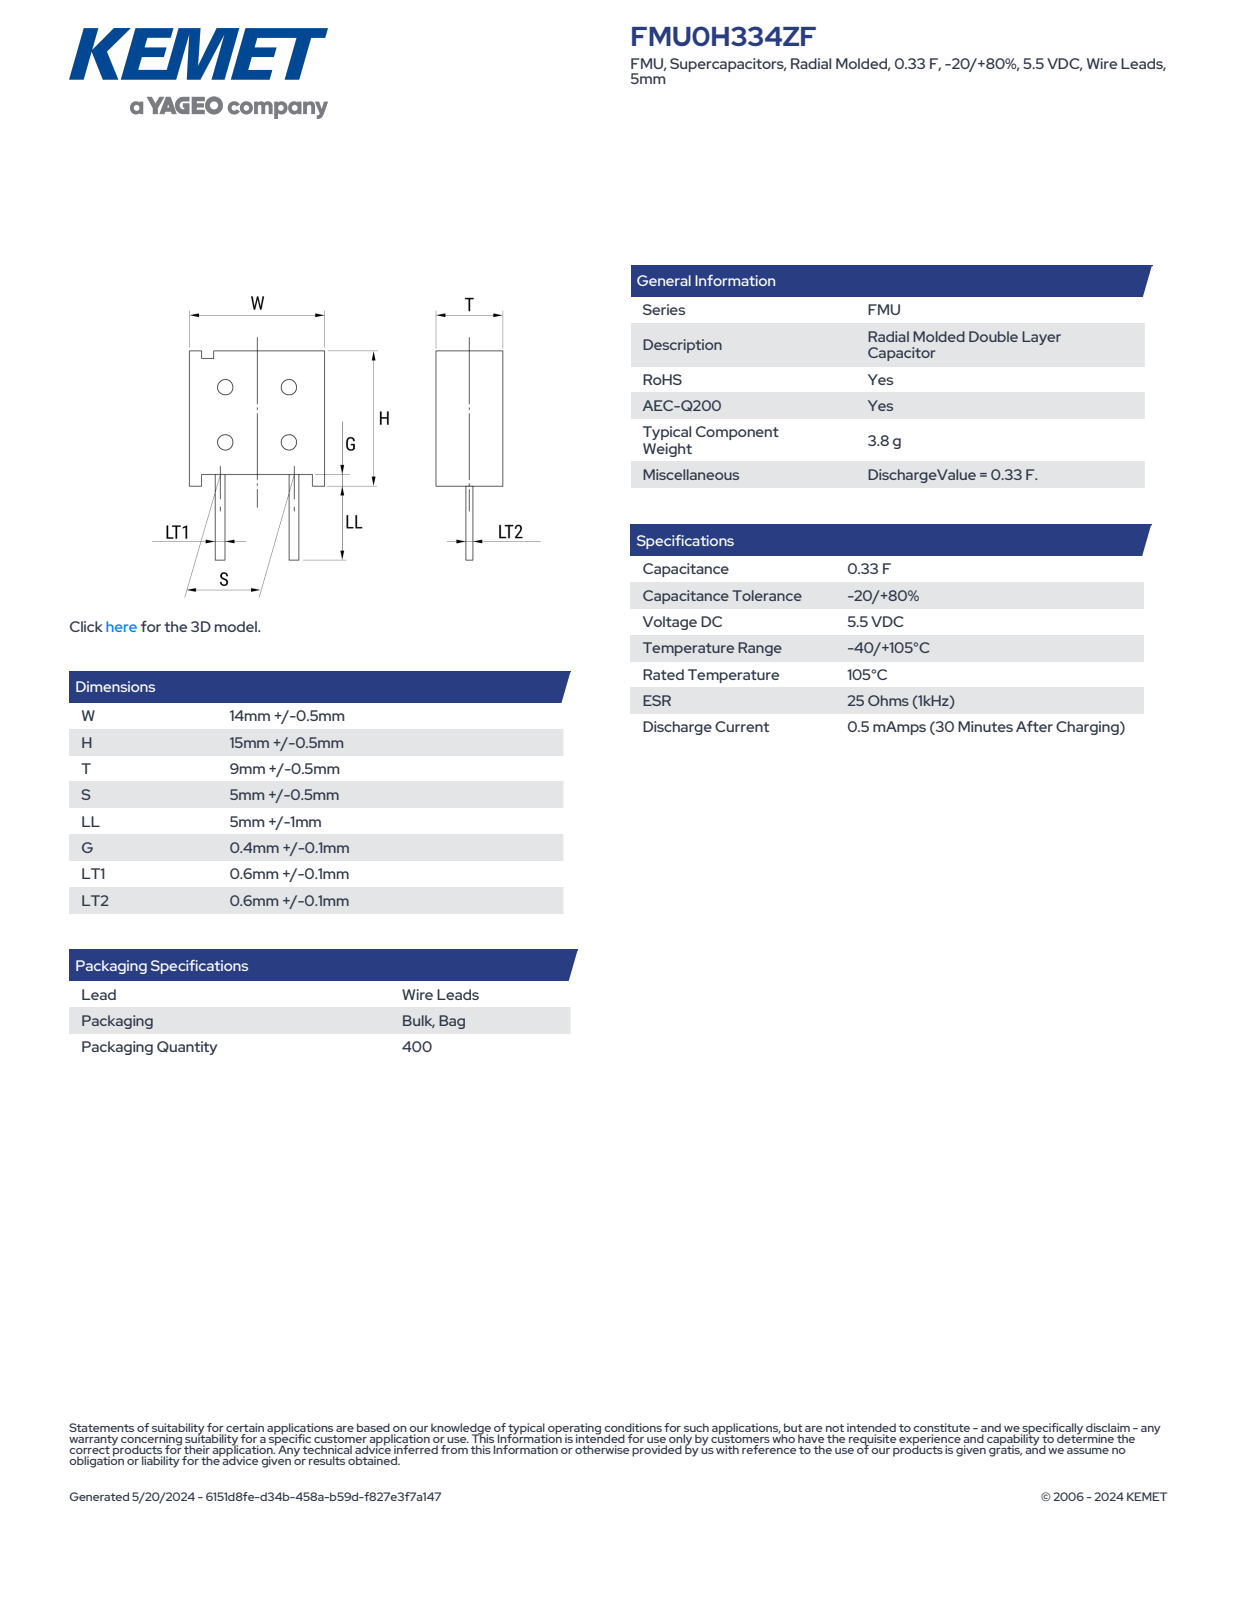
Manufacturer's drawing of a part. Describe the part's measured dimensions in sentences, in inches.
The part is named "CDR_RM_W14.5H15.5T9.5S5LL6G0.5LT10.7LT20.7". Its 3-D file was written by "SolidWorks 2014 (AUTOMOTIVE_DESIGN)". It is 4 solids with 79 faces: 77 planar, 2 cylindrical and 0 other. Overall it measures 0.846 by 0.571 by 0.374 inches. Its volume is 0.127 cubic inches and its surface area 1.697 square inches. Partial cylindrical surfaces (rounded edges, fillets, slot ends): 2 of radius 0.02. The main face-to-face distances are 0.374, 0.571, 0.591, 0.173, 0.201, 0.028, 0.1, 0.37, 0.398, 0.197.
